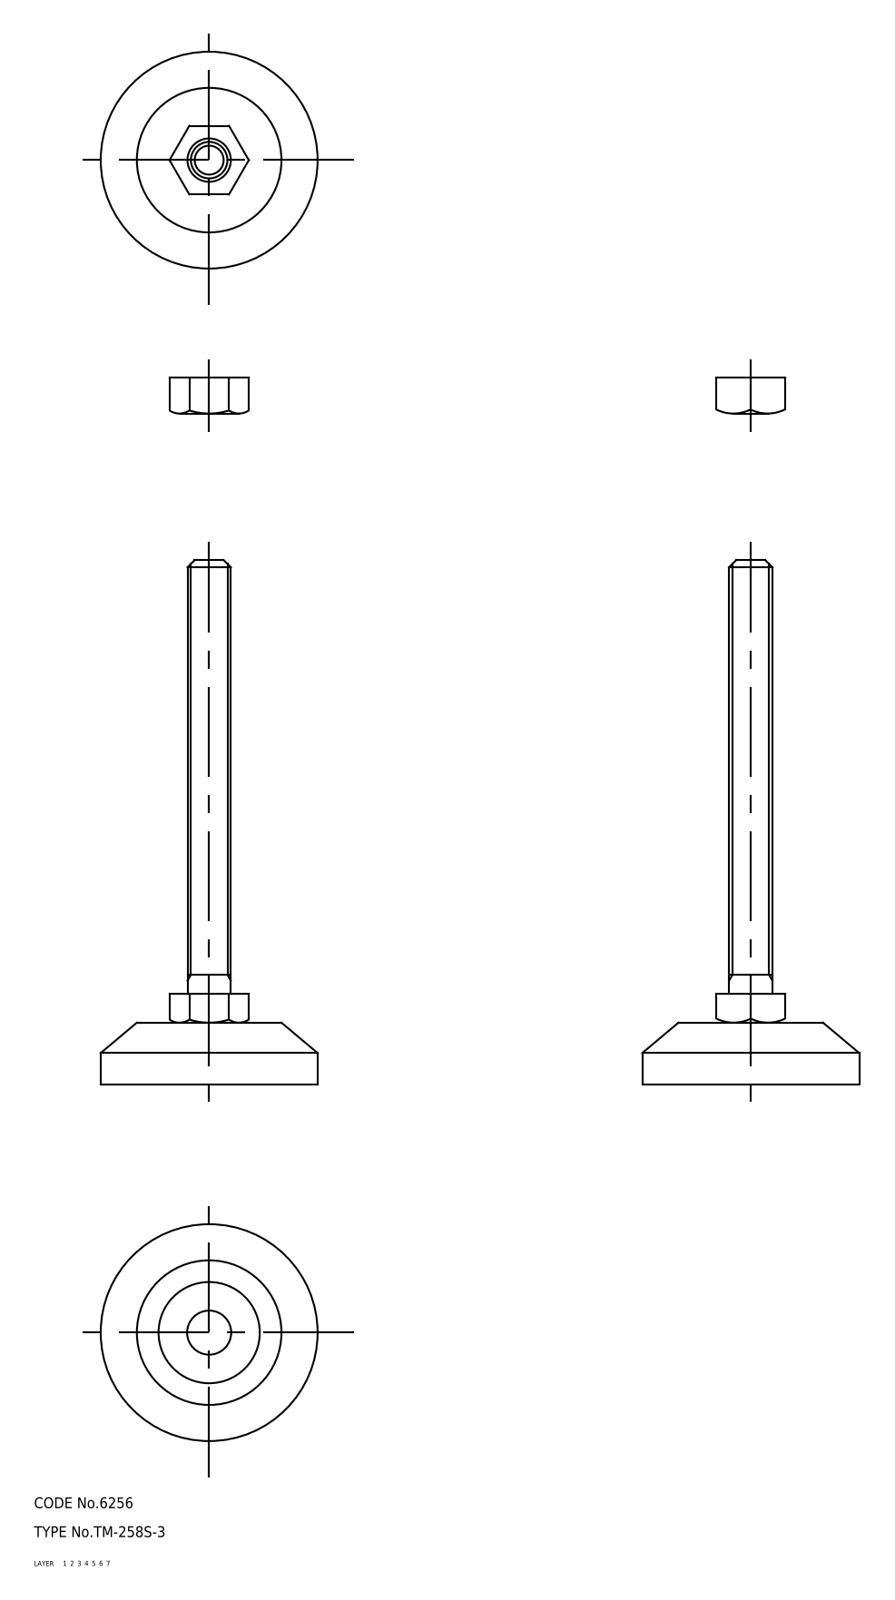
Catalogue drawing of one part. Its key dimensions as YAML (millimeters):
part_name: "67112542; 67112555; 67112568"
step_written_by: "CADfix (AUTOMOTIVE_DESIGN)"
units: millimeters
bodies: {solids: 3, faces: 75, planar: 0, cylindrical: 0, other: 75}
overall_size: [145, 60, 60]
volume: 49746
surface_area: 16326
